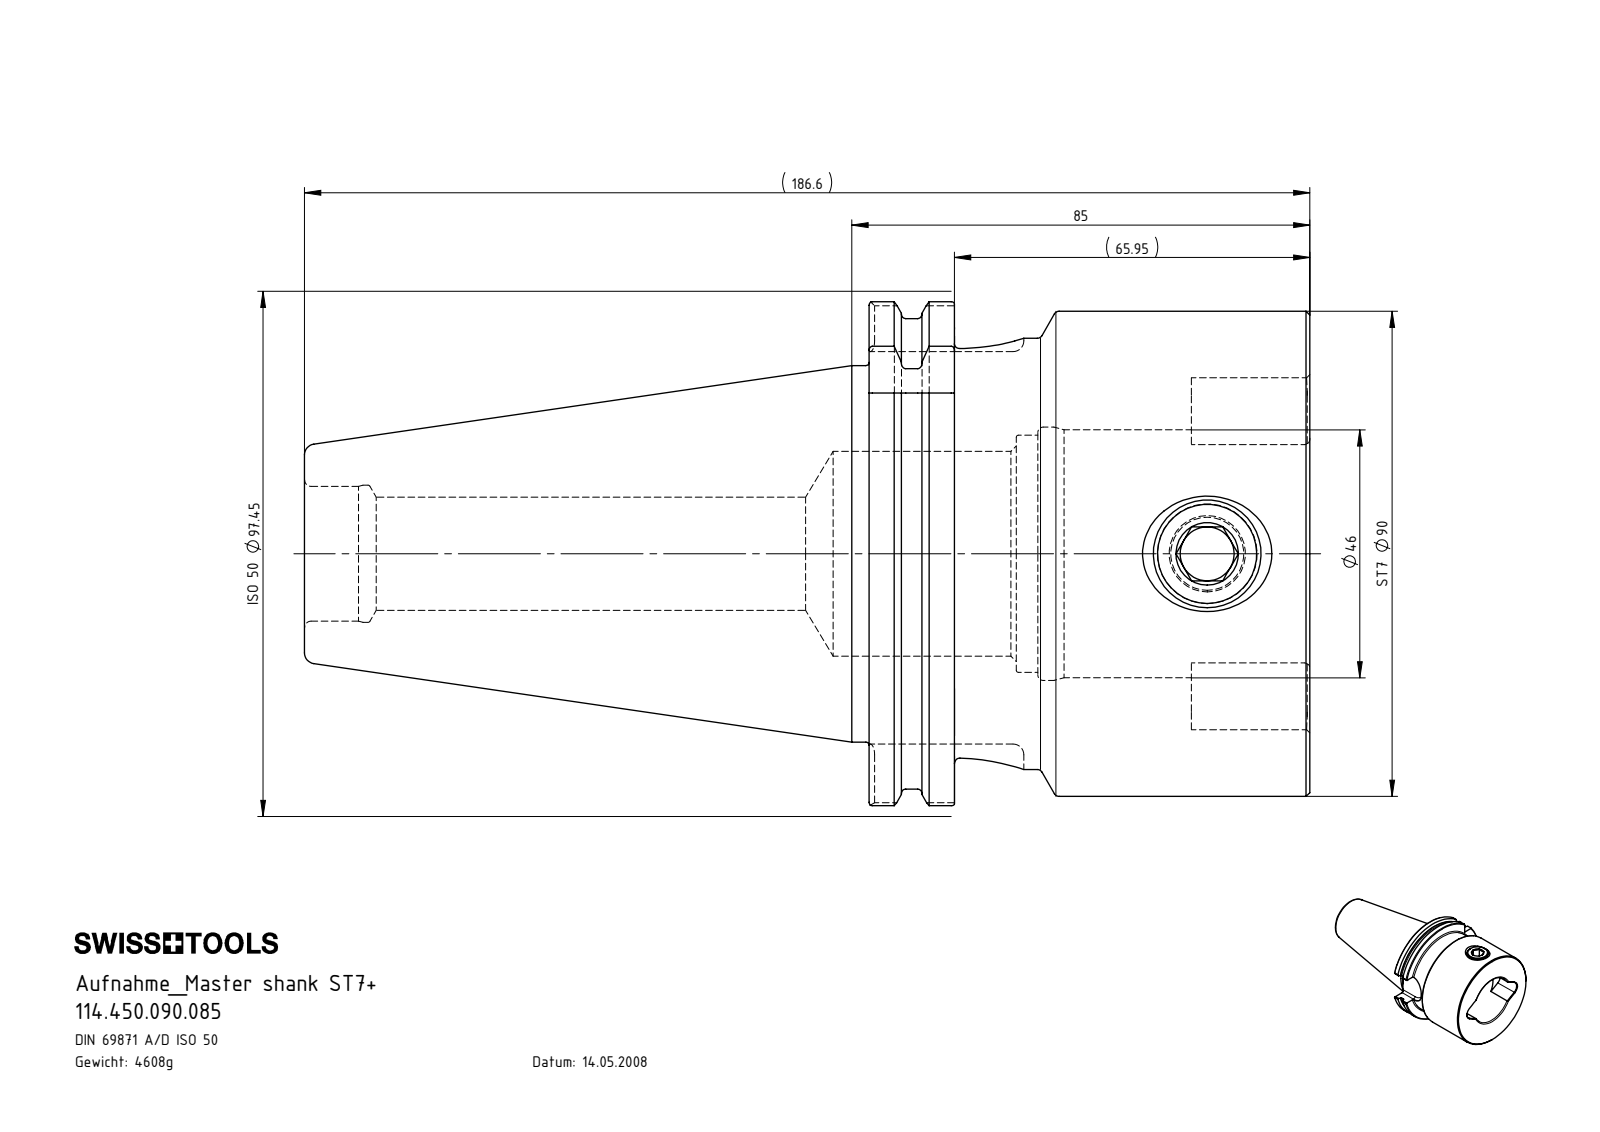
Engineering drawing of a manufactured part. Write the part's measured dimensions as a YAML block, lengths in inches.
part_name: "SK5.ST7.K01.085; ST7-ER1.001.029_A; SK5-ST7.K01.085_B"
step_written_by: "SolidWorks 2017 (AUTOMOTIVE_DESIGN)"
units: inches
bodies: {solids: 2, faces: 140, planar: 56, cylindrical: 34, other: 50}
overall_size: [7.346, 3.837, 3.681]
volume: 35.82
surface_area: 119.3
round_holes:
  - {diameter: 0.394, count: 1}
  - {diameter: 0.728, count: 1}
  - {diameter: 0.827, count: 1}
  - {diameter: 0.984, count: 1}
  - {diameter: 1.002, count: 1}
  - {diameter: 1.496, count: 1}
  - {diameter: 1.732, count: 1}
  - {diameter: 1.811, count: 1}
  - {diameter: 1.85, count: 1}
round_bosses_or_shafts:
  - {diameter: 3.583, count: 1}
  - {diameter: 3.543, count: 1}
  - {diameter: 3.15, count: 1}
  - {diameter: 2.75, count: 1}
  - {diameter: 0.787, count: 1}
partial_cylinders:
  - {radius: 0.079, count: 8}
  - {radius: 0.256, count: 2}
  - {radius: 0.506, count: 1}
  - {radius: 1.919, count: 1}
face_to_face_distances: [3.22, 0.624, 2.596, 2.866, 4.126, 4.75, 7.346, 1.541, 1.28, 6.48]
